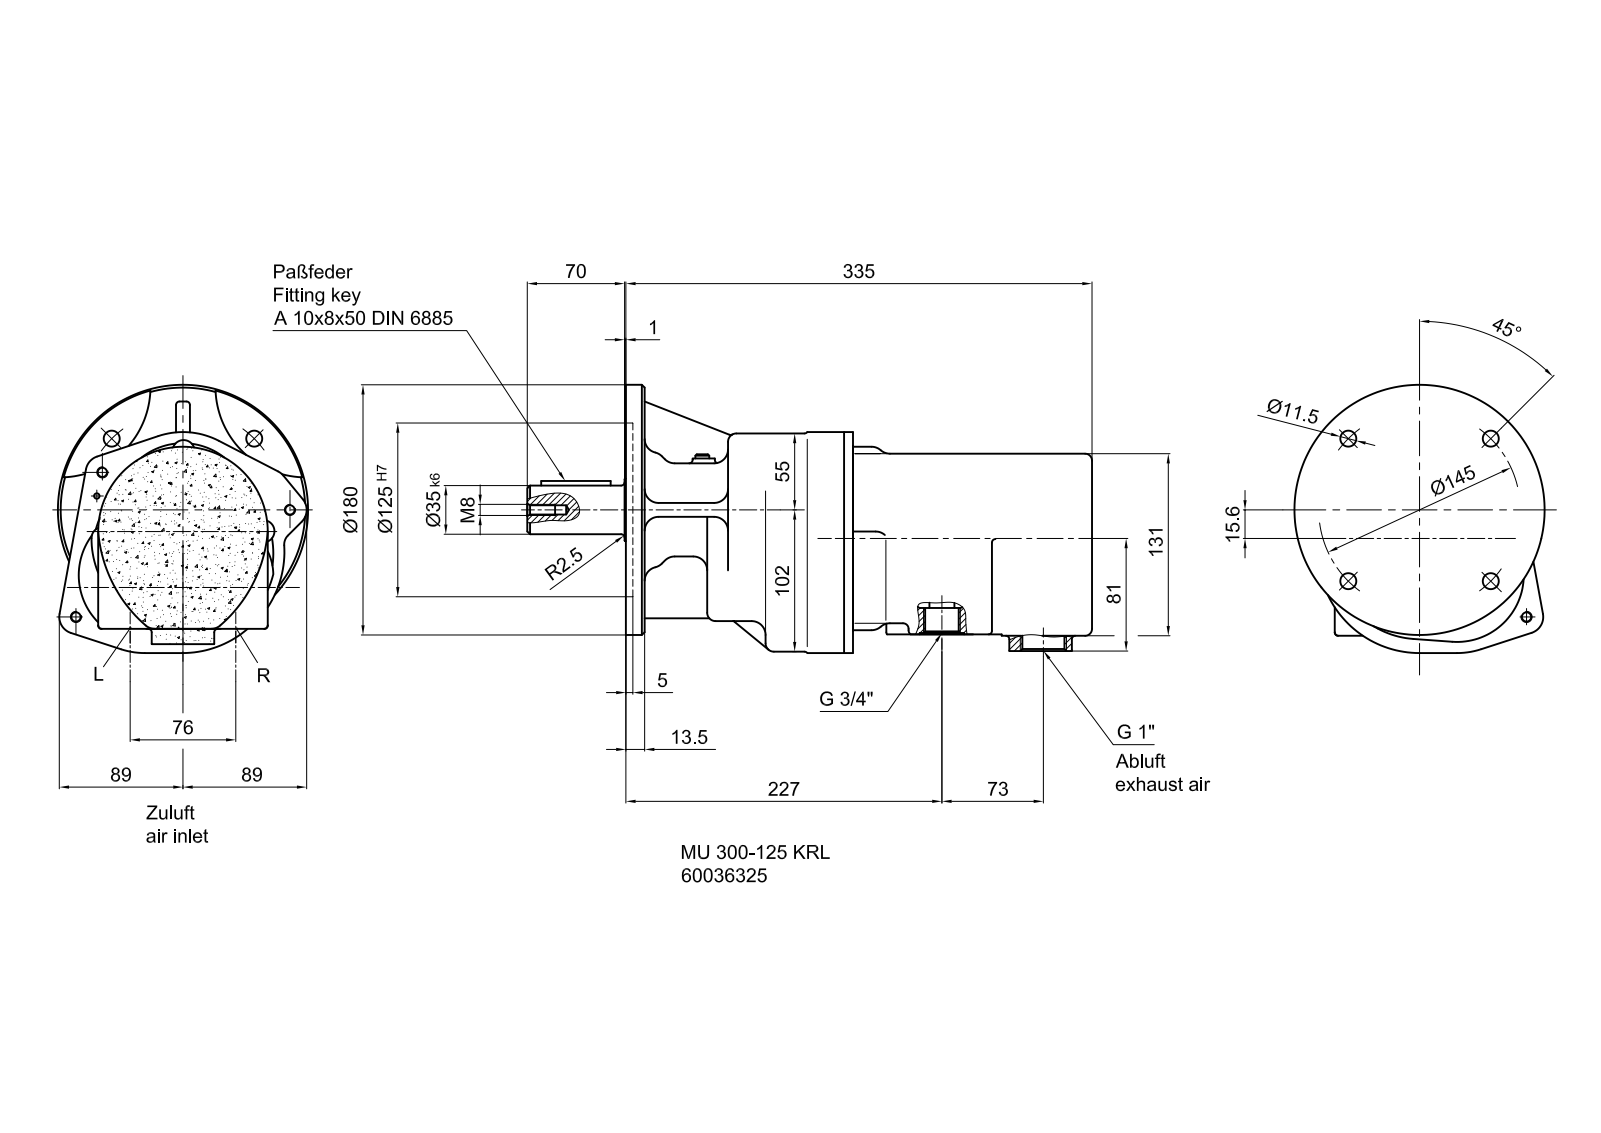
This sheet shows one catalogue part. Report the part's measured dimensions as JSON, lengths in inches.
{"part_name": "MU 300-125 KRL_60036325", "step_written_by": "Autodesk Inventor 2018 (CONFIG_CONTROL_DESIGN)", "units": "inches", "bodies": {"solids": 2, "faces": 937, "planar": 331, "cylindrical": 323, "other": 283}, "overall_size": [16.012, 7.598, 7.087], "volume_in3": 279.1, "surface_area_in2": 469.6, "round_holes": [[0.194, 4], [0.262, 4], [0.453, 4], [0.335, 3], [0.374, 3], [0.256, 2], [0.95, 2], [1.26, 2], [0.098, 1], [0.11, 1], [0.154, 1], [0.157, 1]], "round_bosses_or_shafts": [[0.583, 3], [0.512, 3], [0.315, 3], [7.087, 1], [4.803, 1], [1.772, 1], [1.378, 1], [0.63, 1]], "partial_cylinders_radius": [[0.079, 30], [0.098, 29], [0.157, 20], [0.118, 12], [0.236, 12], [0.394, 12], [0.039, 6], [0.059, 6]], "face_to_face_distances": [0.197, 0.039, 13.224, 0.295, 13.028, 6.772, 6.256, 6.453, 12.693, 5.921], "hole_center_spacings": [1.181, 2.855, 3.217, 4.037, 2.258, 2.992, 5.439, 1.083]}
